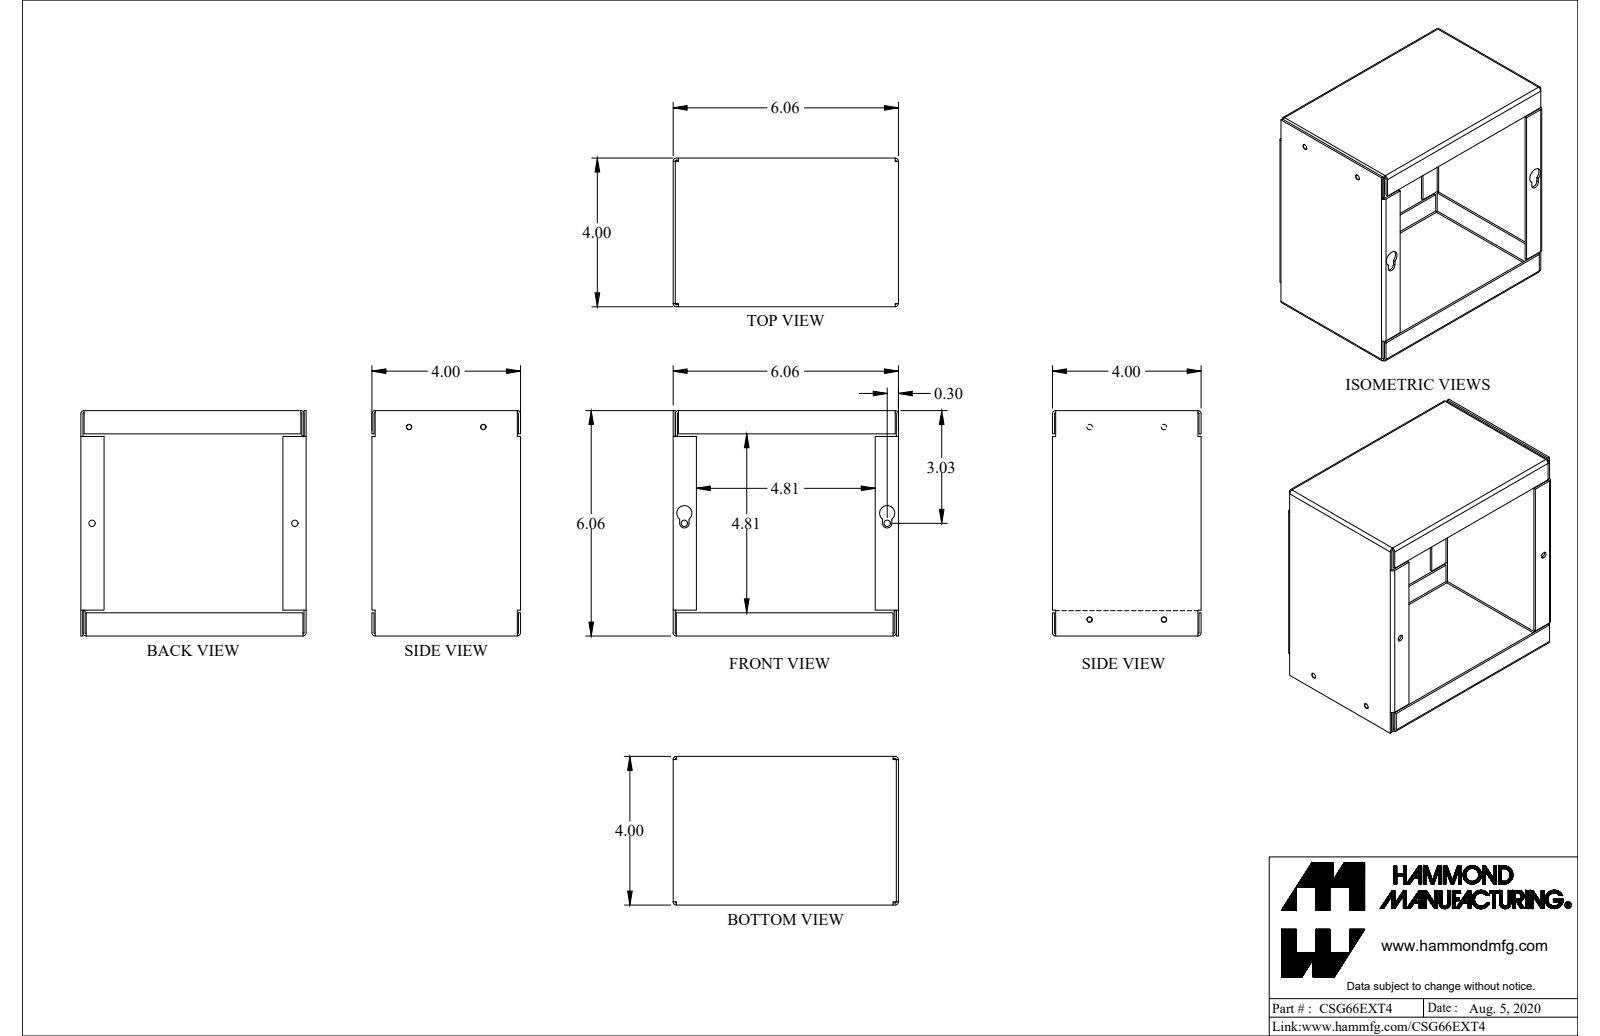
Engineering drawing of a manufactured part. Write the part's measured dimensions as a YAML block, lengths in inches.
part_name: "CSG66EXT4"
step_written_by: "SolidWorks 2021 (AUTOMOTIVE_DESIGN)"
units: inches
bodies: {solids: 2, faces: 114, planar: 76, cylindrical: 38, other: 0}
overall_size: [6.063, 6.063, 4]
volume: 6.976
surface_area: 249.4
round_holes:
  - {diameter: 0.145, count: 4}
  - {diameter: 0.17, count: 2}
round_bosses_or_shafts:
  - {diameter: 0.131, count: 4}
partial_cylinders:
  - {radius: 0.029, count: 12}
  - {radius: 0.086, count: 12}
  - {radius: 0.125, count: 2}
  - {radius: 0.203, count: 2}
face_to_face_distances: [6.006, 0.057, 0.057, 5.948, 6.063, 6.062, 5.949, 3.943, 4, 3.886]
hole_center_spacings: [2, 5.18, 5.553, 5.459]
